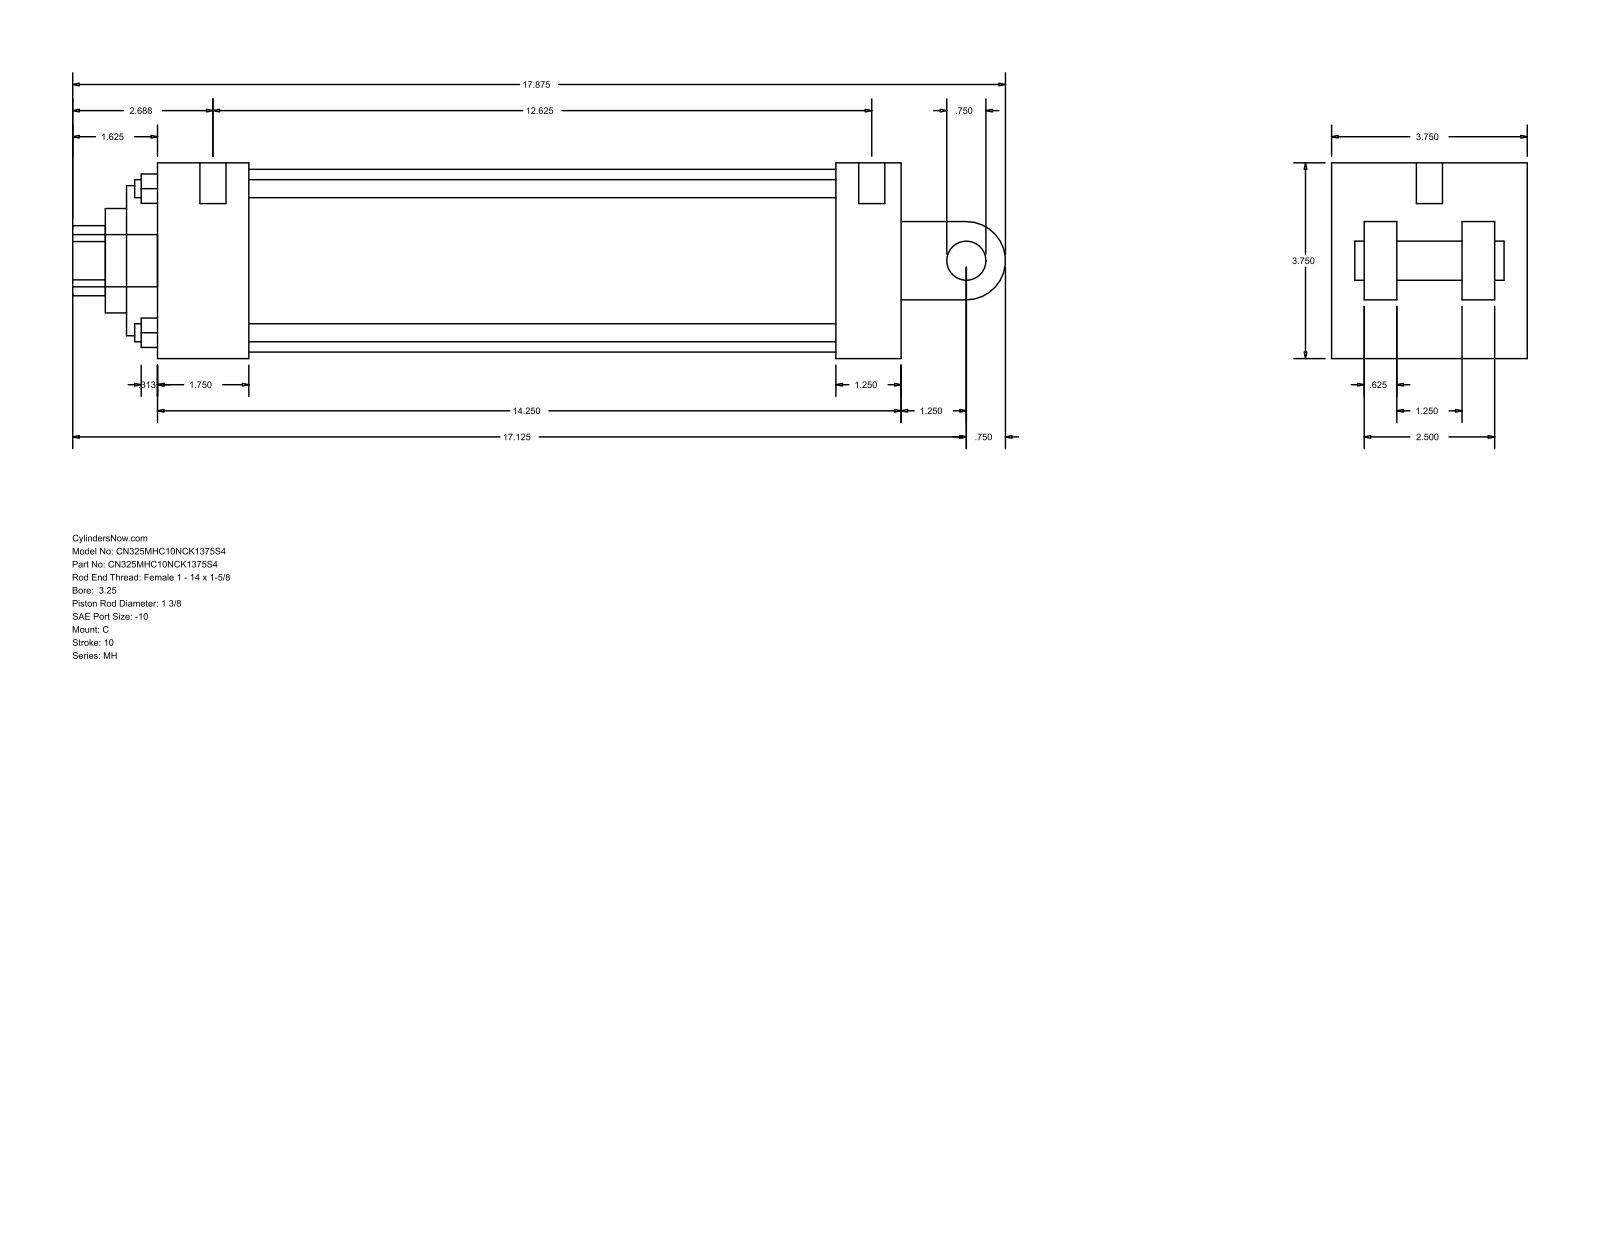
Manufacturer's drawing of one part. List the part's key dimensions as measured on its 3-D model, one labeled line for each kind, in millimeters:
Part name (STEP PRODUCT): MH_C__0325_1.375
STEP written by: GSSL Pune (CONFIG_CONTROL_DESIGN)
Units: millimetres
Bodies: 0 solids, 101 faces (71 planar, 30 cylindrical, 0 other)
Overall size (bounding box): 454.02 × 95.25 × 95.25
Round holes (diameter × count): ⌀8.76 ×4, ⌀5.56 ×2, ⌀12.7 ×1, ⌀34.92 ×1, ⌀50.8 ×1, ⌀73.03 ×1, ⌀88.9 ×1
Round bosses / shafts (diameter × count): ⌀5.56 ×2, ⌀25.4 ×1, ⌀19.05 ×1, ⌀12.7 ×1
Partial cylindrical surfaces — rounded edges, fillets, slot ends (radius × count): R17.06 ×1, R19.05 ×1
Main face-to-face distances: 95.24, 15.87, 361.96, 63.5, 79.37, 31.74, 47.63, 44.45, 330.21, 285.76
Hole centre spacings: 49.57, 70.1, 99.14, 4.76
